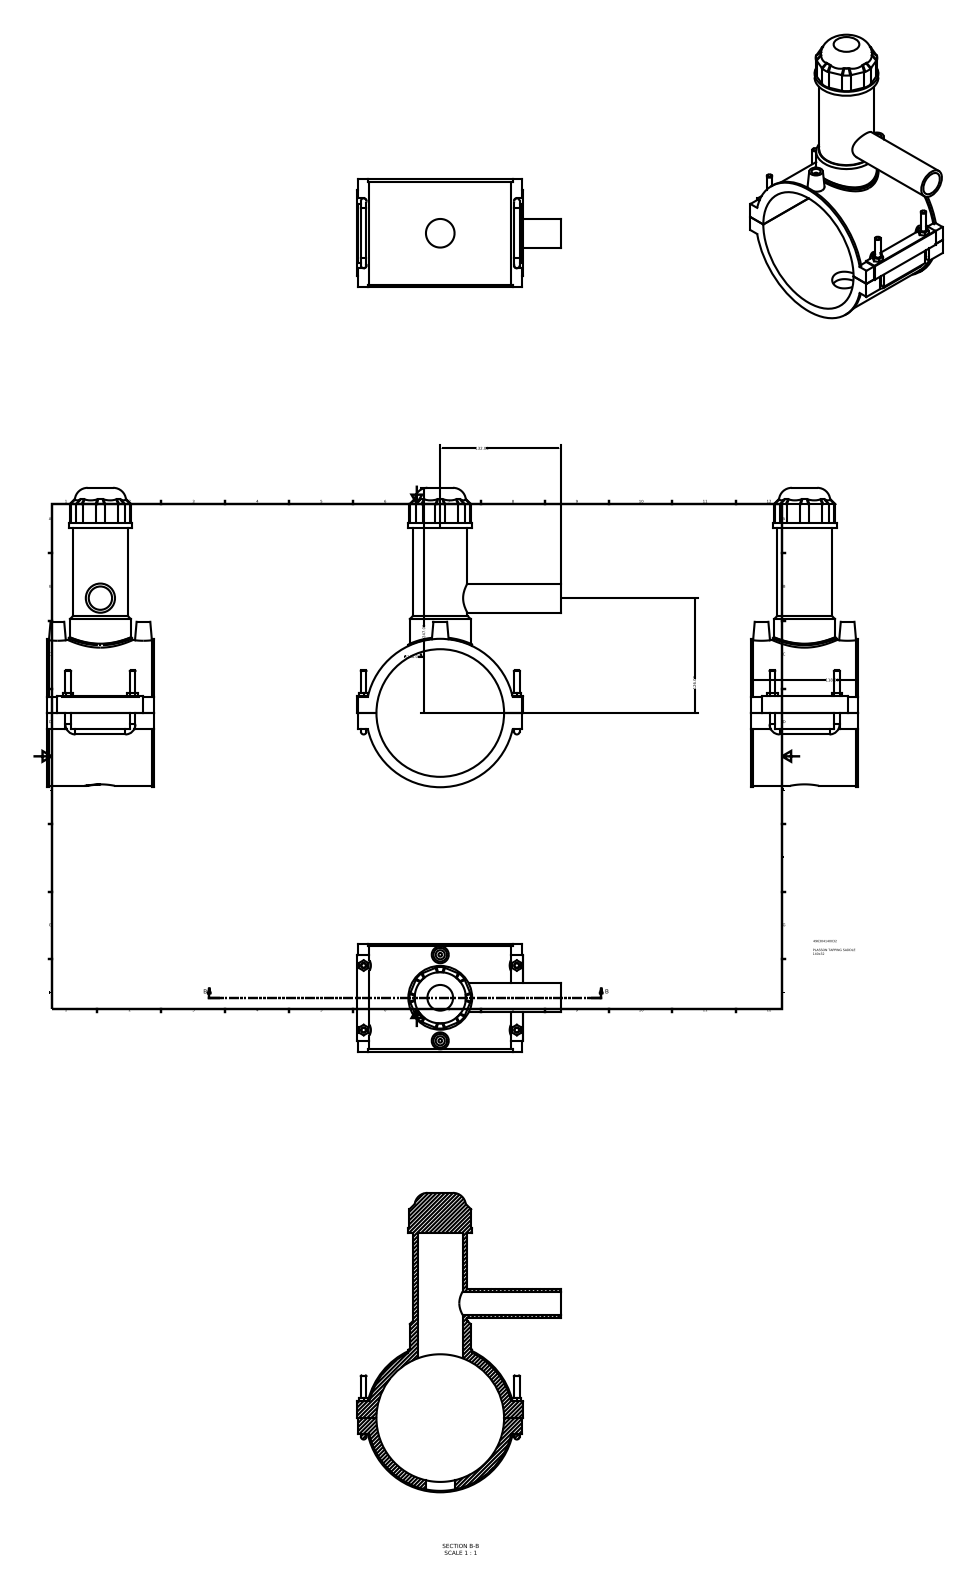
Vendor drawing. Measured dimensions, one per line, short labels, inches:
name: 496304140032
written by: Autodesk Inventor 2015 (AUTOMOTIVE_DESIGN)
unit: in
bodies: 1 solid, 207 faces (118 planar, 48 cylindrical, 41 other)
size: 12.929 × 8.78 × 4.646
volume: 56.3 in³; area: 343 in²
holes: 2× ⌀0.394, 1× ⌀1.008, 1× ⌀1.235, 1× ⌀1.929, 1× ⌀5.512
bosses: 6× ⌀0.236, 2× ⌀0.157, 1× ⌀6.409, 1× ⌀6.283, 1× ⌀2.756, 1× ⌀2.618, 1× ⌀2.343, 1× ⌀1.26
rounds: 8× R0.551, 4× R0.118, 4× R0.295, 1× R0.02, 1× R3.267
face distances: 4.646, 0.039, 7.126, 0.687, 0.691, 7.984, 7.98, 8.671, 7.087, 1.417
hole spacings: 1.858, 3.717
